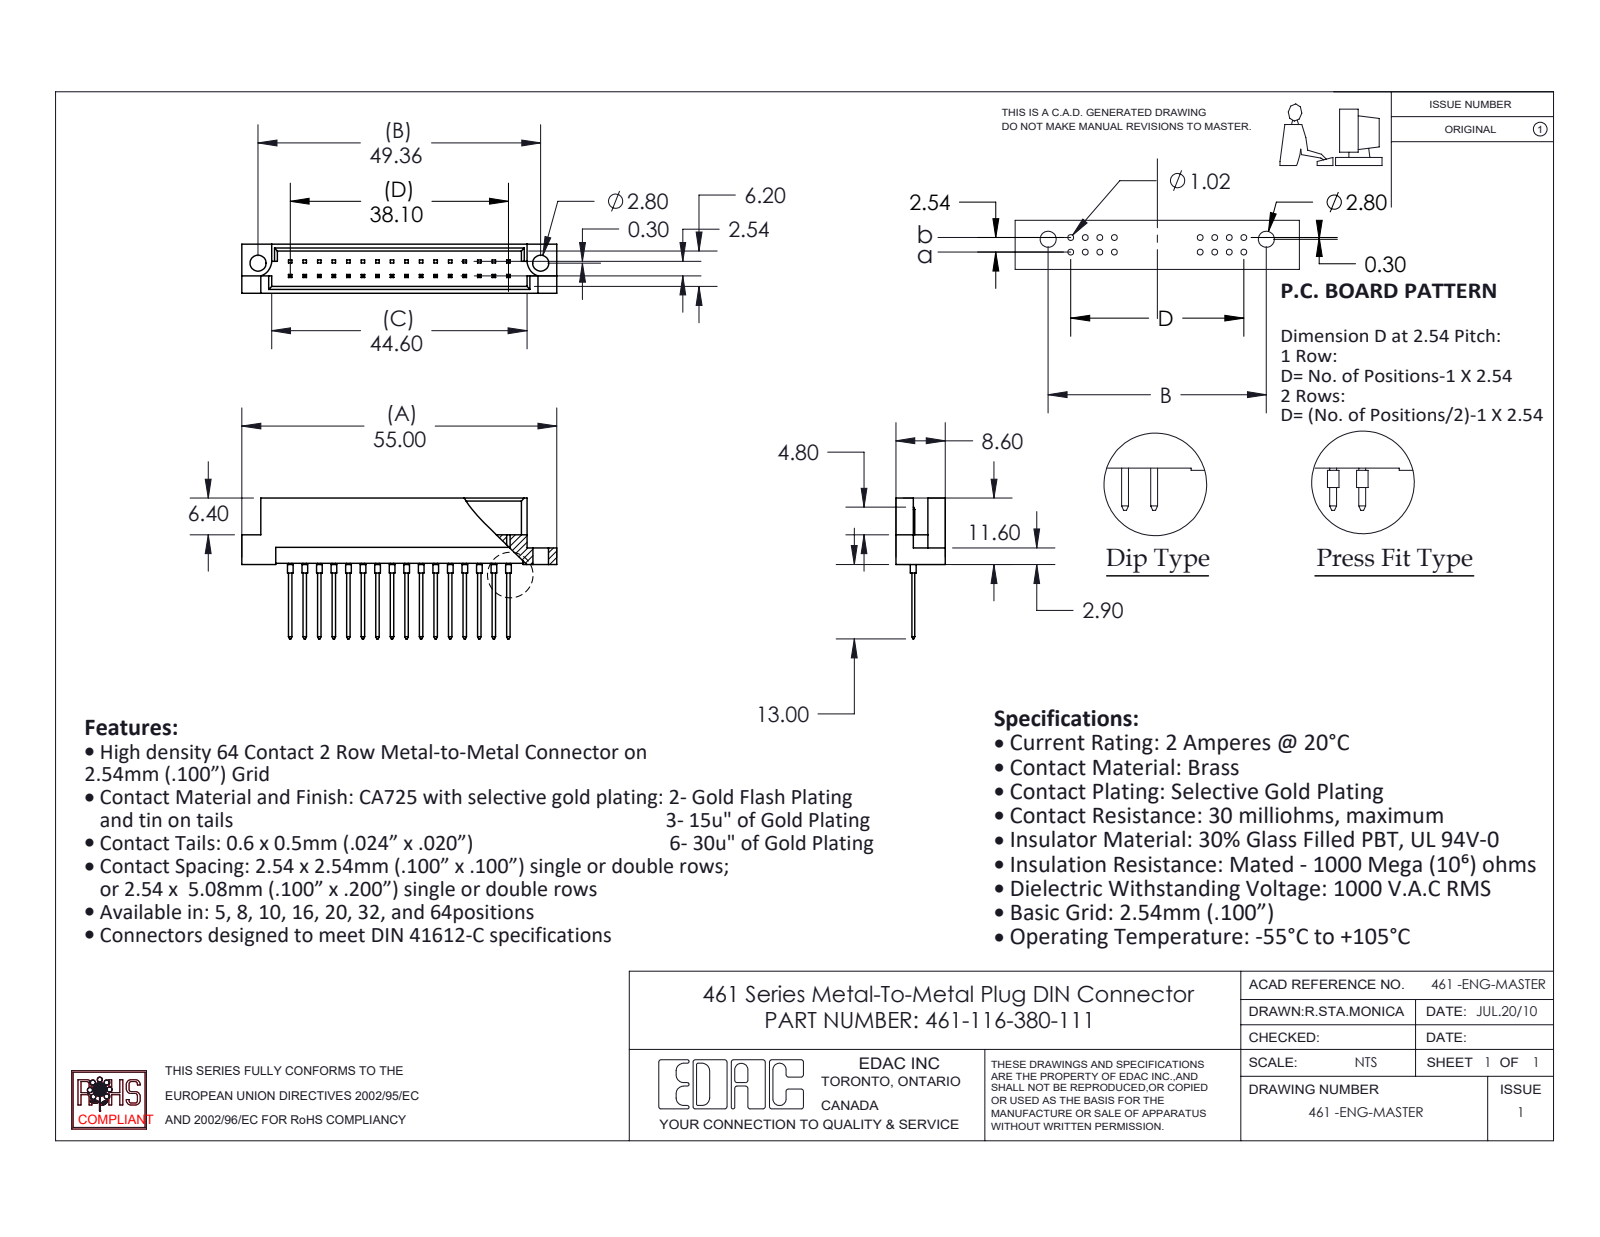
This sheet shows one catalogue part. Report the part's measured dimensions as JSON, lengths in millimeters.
{"part_name": "461-290_80; 461-116-380-111; 461 Part_32", "step_written_by": "SolidWorks 2020 (CONFIG_CONTROL_DESIGN)", "units": "millimeters", "bodies": {"solids": 17, "faces": 528, "planar": 490, "cylindrical": 38, "other": 0}, "overall_size": [55, 24.6, 8.6], "volume_mm3": 2774, "surface_area_mm2": 4089, "round_holes": [[2.8, 2]], "round_bosses_or_shafts": [[1, 16]], "partial_cylinders_radius": [[2.8, 2]], "face_to_face_distances": [1.2, 7.4, 8.6, 6.2, 2.54, 2.78, 5.82, 1.58, 4.62, 3.28], "hole_center_spacings": [49.36]}
